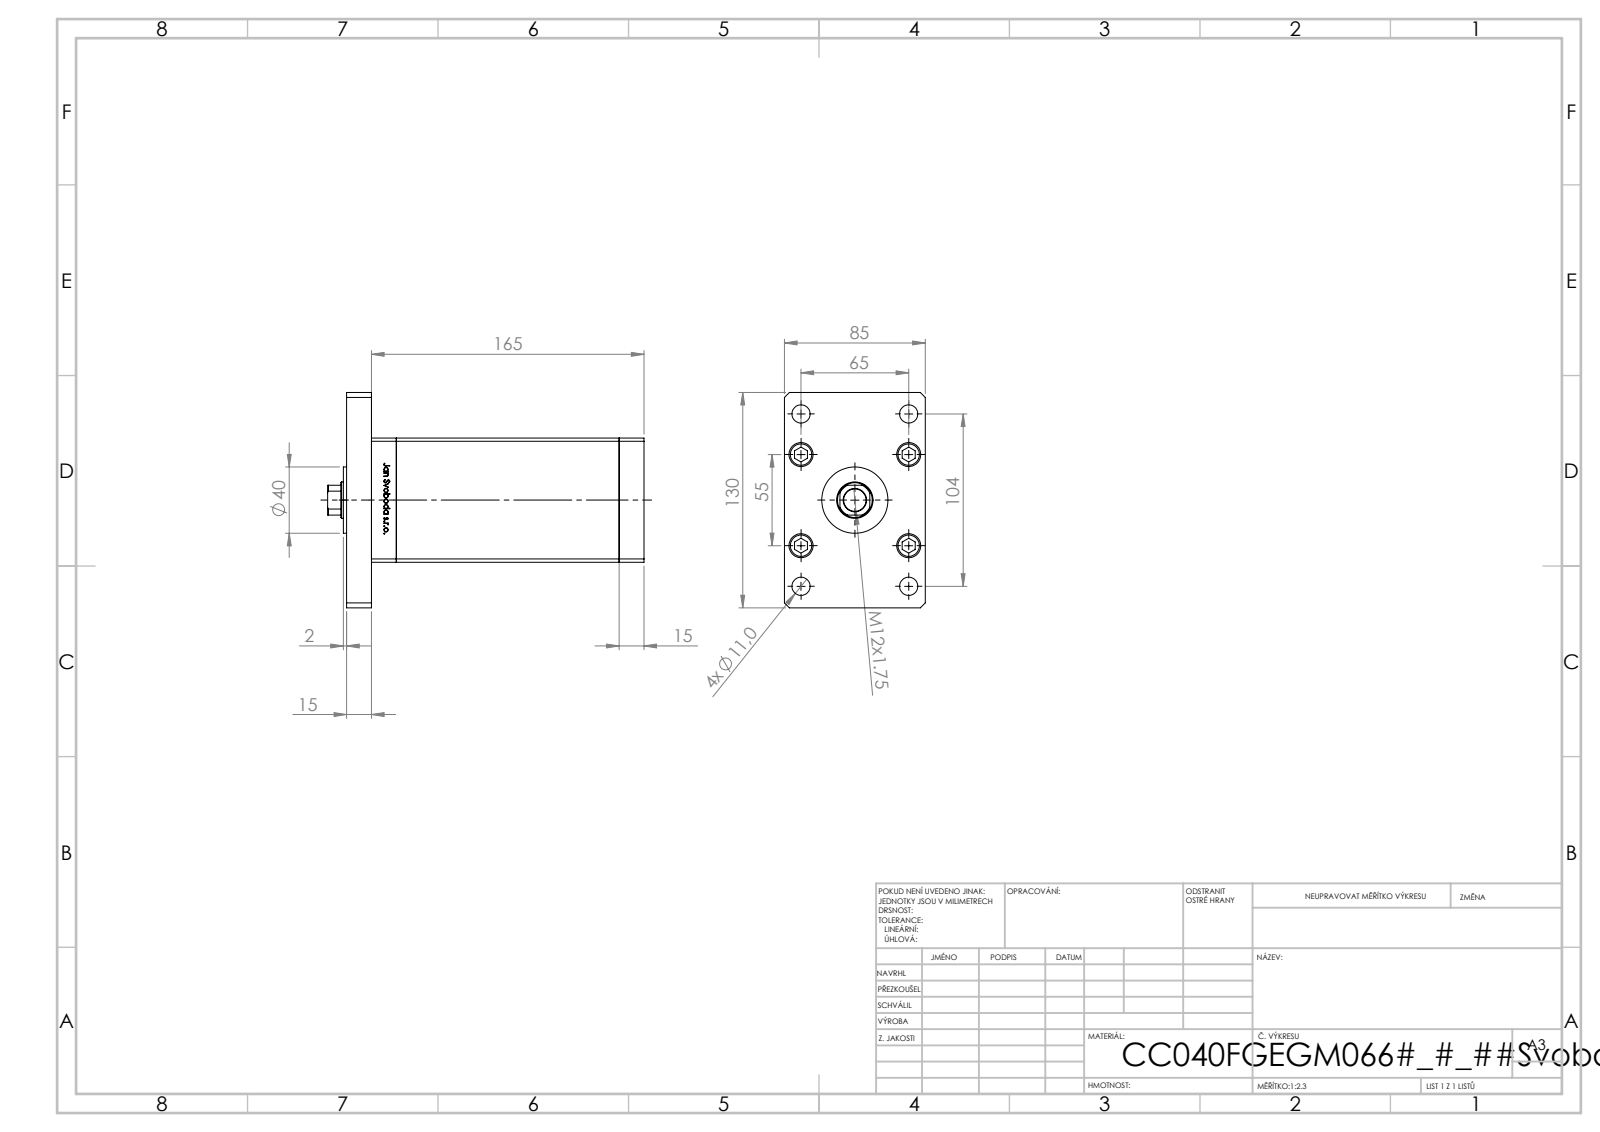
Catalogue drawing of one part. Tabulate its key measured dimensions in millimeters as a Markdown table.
| quantity | value |
| --- | --- |
| part name | V220C_VC_F; V220C_F_MIDDLE; ALLEN BOLT; V220C_F (+2 more) |
| STEP written by | SolidWorks 2019 (CONFIG_CONTROL_DESIGN) |
| units | millimeters |
| bodies | 19 solids, 1310 faces (517 planar, 187 cylindrical, 606 other) |
| overall size | 191 × 130 × 85 |
| volume | 1 091 000 mm³ |
| surface area | 191 407 mm² |
| round holes (diameter × count) | 11 × 9, 15.5 × 5, 10 × 4, 14.5 × 4, 2 × 2, 13.16 × 2, 13.5 × 1, 22 × 1, 23.5 × 1 |
| round bosses / shafts (diameter × count) | 8 × 9, 14.5 × 5, 40 × 1 |
| partial cylindrical surfaces (radius × count) | 0.93 × 2, 10.5 × 1 |
| main face-to-face distances | 15, 149.5, 164.5, 85, 75, 30, 134.5, 179.5, 27.5, 10.5 |
| hole center spacings | 28, 24.5, 42.57, 61.32, 65, 69.46, 79.5, 102.69 |
